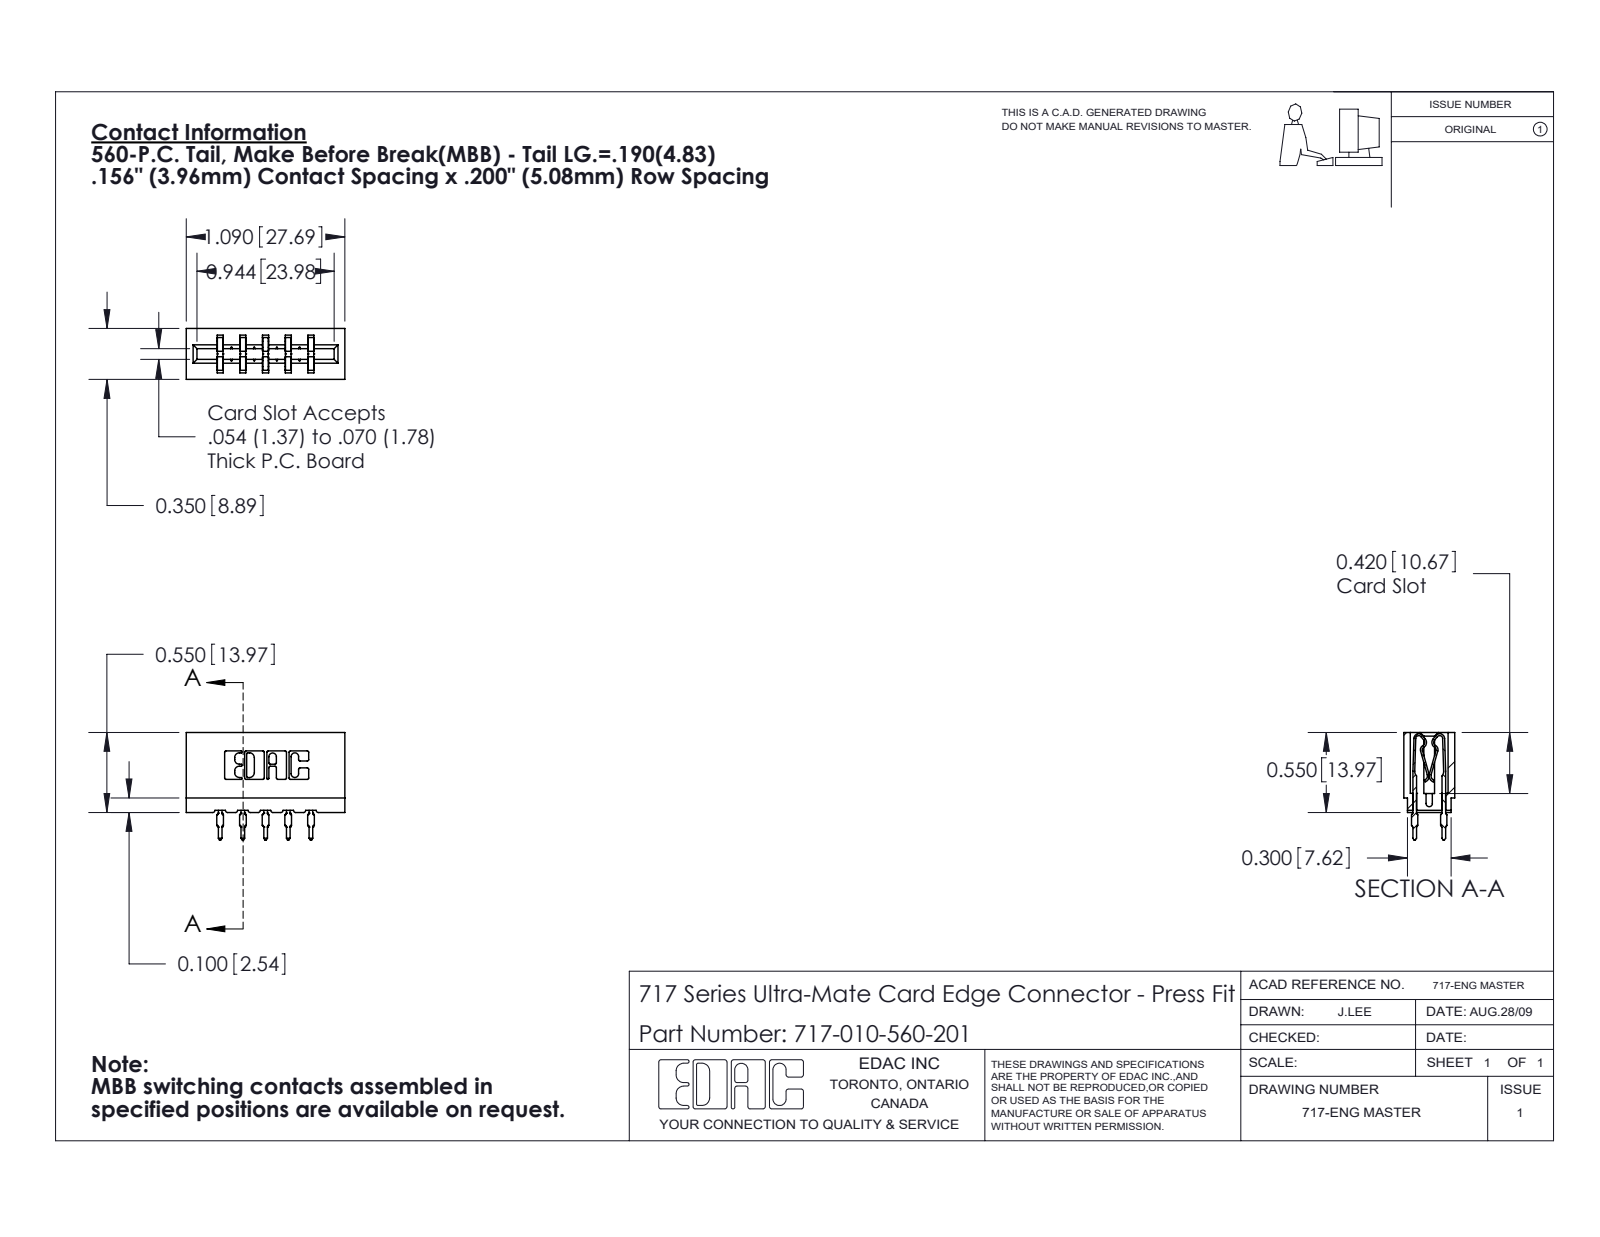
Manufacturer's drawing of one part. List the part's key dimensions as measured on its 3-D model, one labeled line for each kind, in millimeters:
Part name (STEP PRODUCT): 717 Part_Insulator Option - 06; 717-010-560-201; 745-292-001_560
STEP written by: SolidWorks 2020 (CONFIG_CONTROL_DESIGN)
Units: millimetres
Bodies: 11 solids, 1084 faces (569 planar, 255 cylindrical, 260 other)
Overall size (bounding box): 27.7 × 18.8 × 8.9
Volume: 2 590 mm³ · Surface area: 3 639 mm²
Partial cylindrical surfaces — rounded edges, fillets, slot ends (radius × count): R0.3 ×22, R0.5 ×20, R0.4 ×10, R0.1 ×8, R0.3 ×8, R0.2 ×6, R0.8 ×6, R0.7 ×3
Main face-to-face distances: 5.4, 4, 3.5, 8.9, 5, 1.1, 7.9, 11.9, 7.9, 1.9
